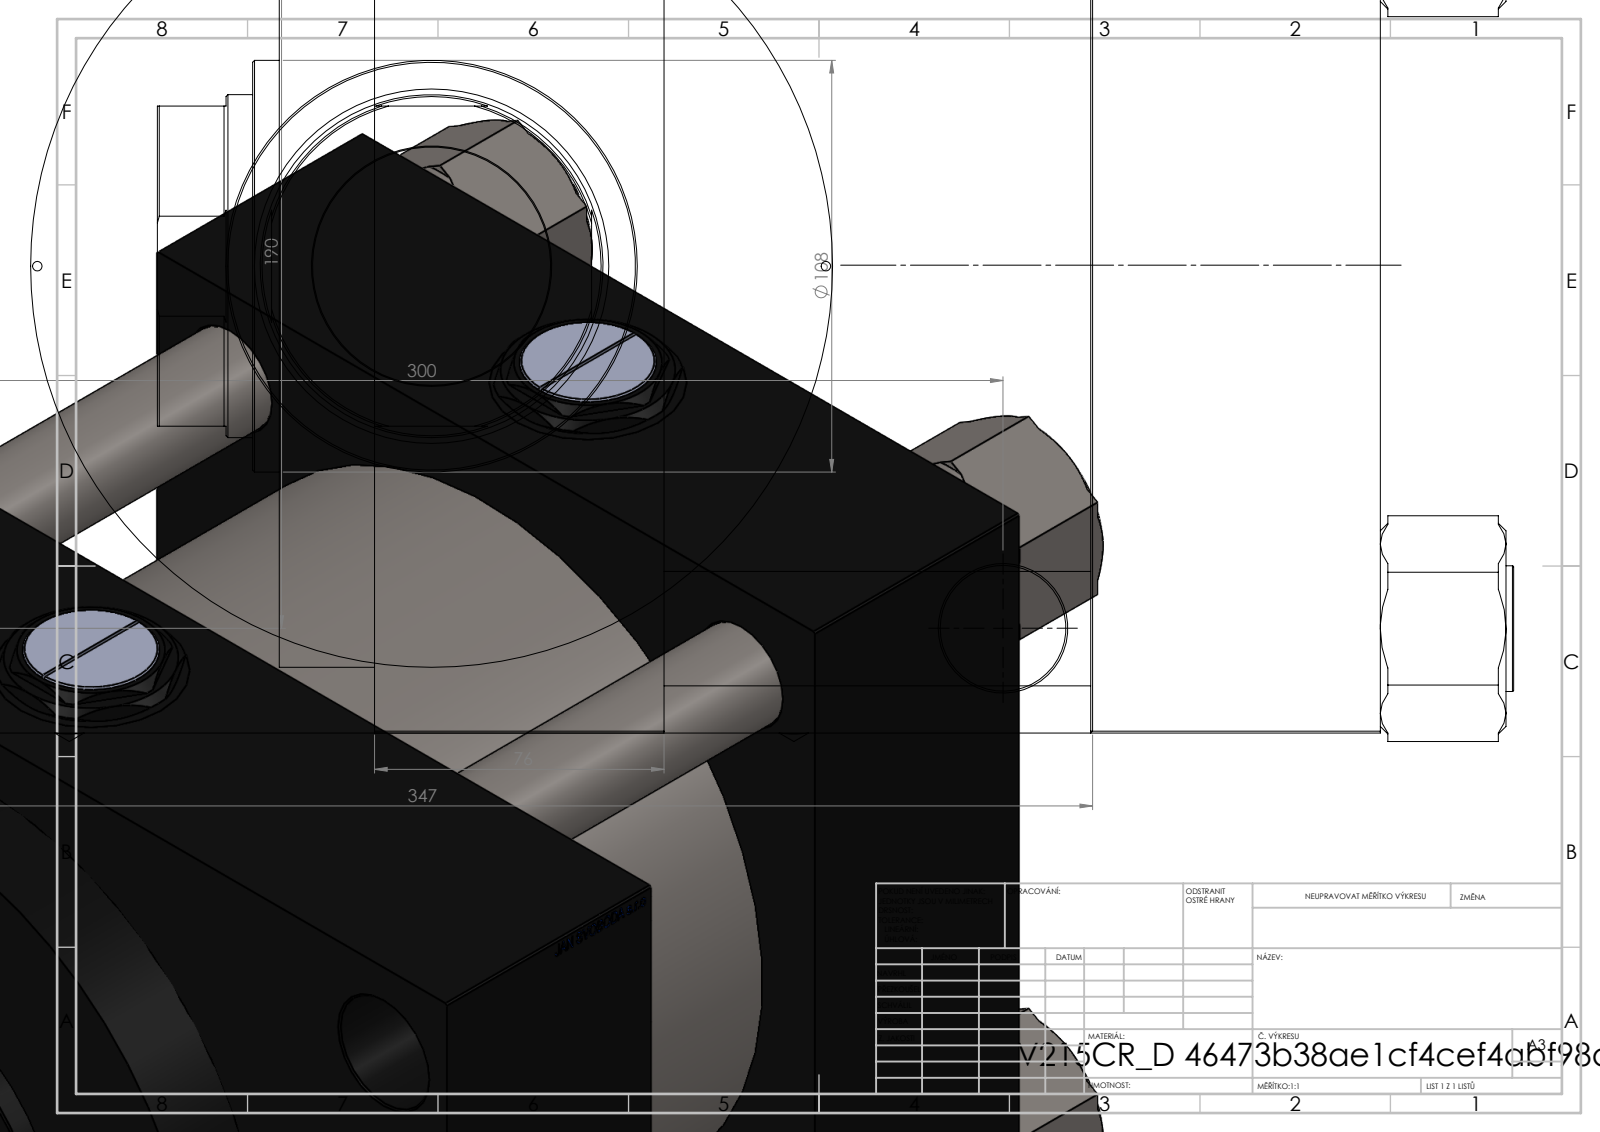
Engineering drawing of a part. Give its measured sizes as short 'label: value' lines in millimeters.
name: V215CR_D_Body; V215_VC_A; NUT_M5_D; Zatka_pro_OIL_PORT (+2 more)
written by: SolidWorks 2019 (CONFIG_CONTROL_DESIGN)
unit: mm
bodies: 13 solids, 1254 faces (593 planar, 101 cylindrical, 560 other)
size: 356 × 347 × 254.22
volume: 14 580 000 mm³; area: 1 114 000 mm²
holes: 4× ⌀30, 4× ⌀33, 4× ⌀41.92, 4× ⌀52, 3× ⌀7, 2× ⌀2.5, 1× ⌀62.5, 1× ⌀90, 1× ⌀93, 1× ⌀146, 1× ⌀200, 1× ⌀210.5
bosses: 4× ⌀33, 1× ⌀206, 1× ⌀108
rounds: 1× R44
face distances: 76, 188, 112, 245, 264, 245.74, 169.74, 57.74, 18.26, 51
hole spacings: 54.9, 95.47, 105.77, 134.49, 177.55, 190.2, 197.87, 220.2
